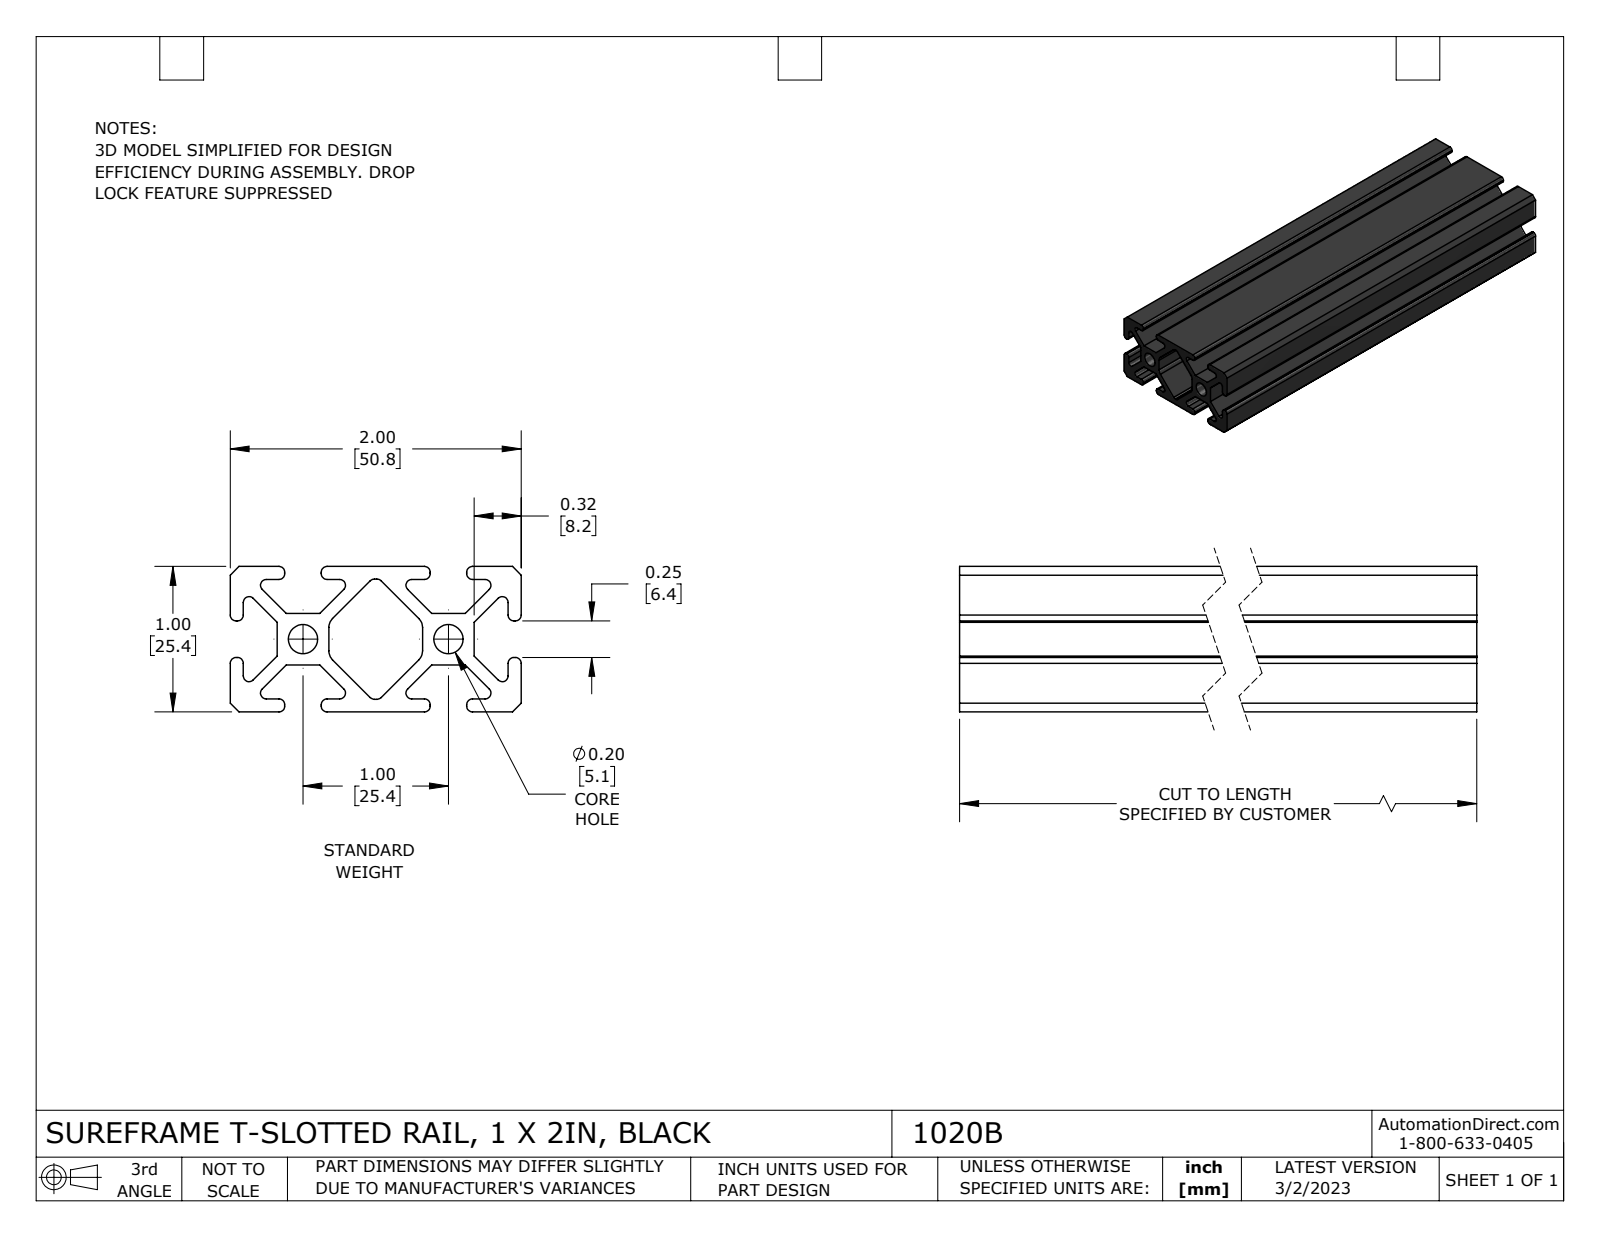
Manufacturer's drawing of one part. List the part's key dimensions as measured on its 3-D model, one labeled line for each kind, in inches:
Part name (STEP PRODUCT): 1020B
STEP written by: SolidWorks 2021 (CONFIG_CONTROL_DESIGN)
Units: inches
Bodies: 1 solid, 120 faces (66 planar, 54 cylindrical, 0 other)
Overall size (bounding box): 6 × 2 × 1
Volume: 4.825 in³ · Surface area: 93.66 in²
Round holes (diameter × count): ⌀0.201 ×2
Partial cylindrical surfaces — rounded edges, fillets, slot ends (radius × count): R0.04 ×36, R0.044 ×4, R0.087 ×4
Main face-to-face distances: 0.087, 0.707, 0.323, 1, 0.62, 0.09, 0.233, 0.794, 0.677, 0.91
Hole centre spacings: 1
